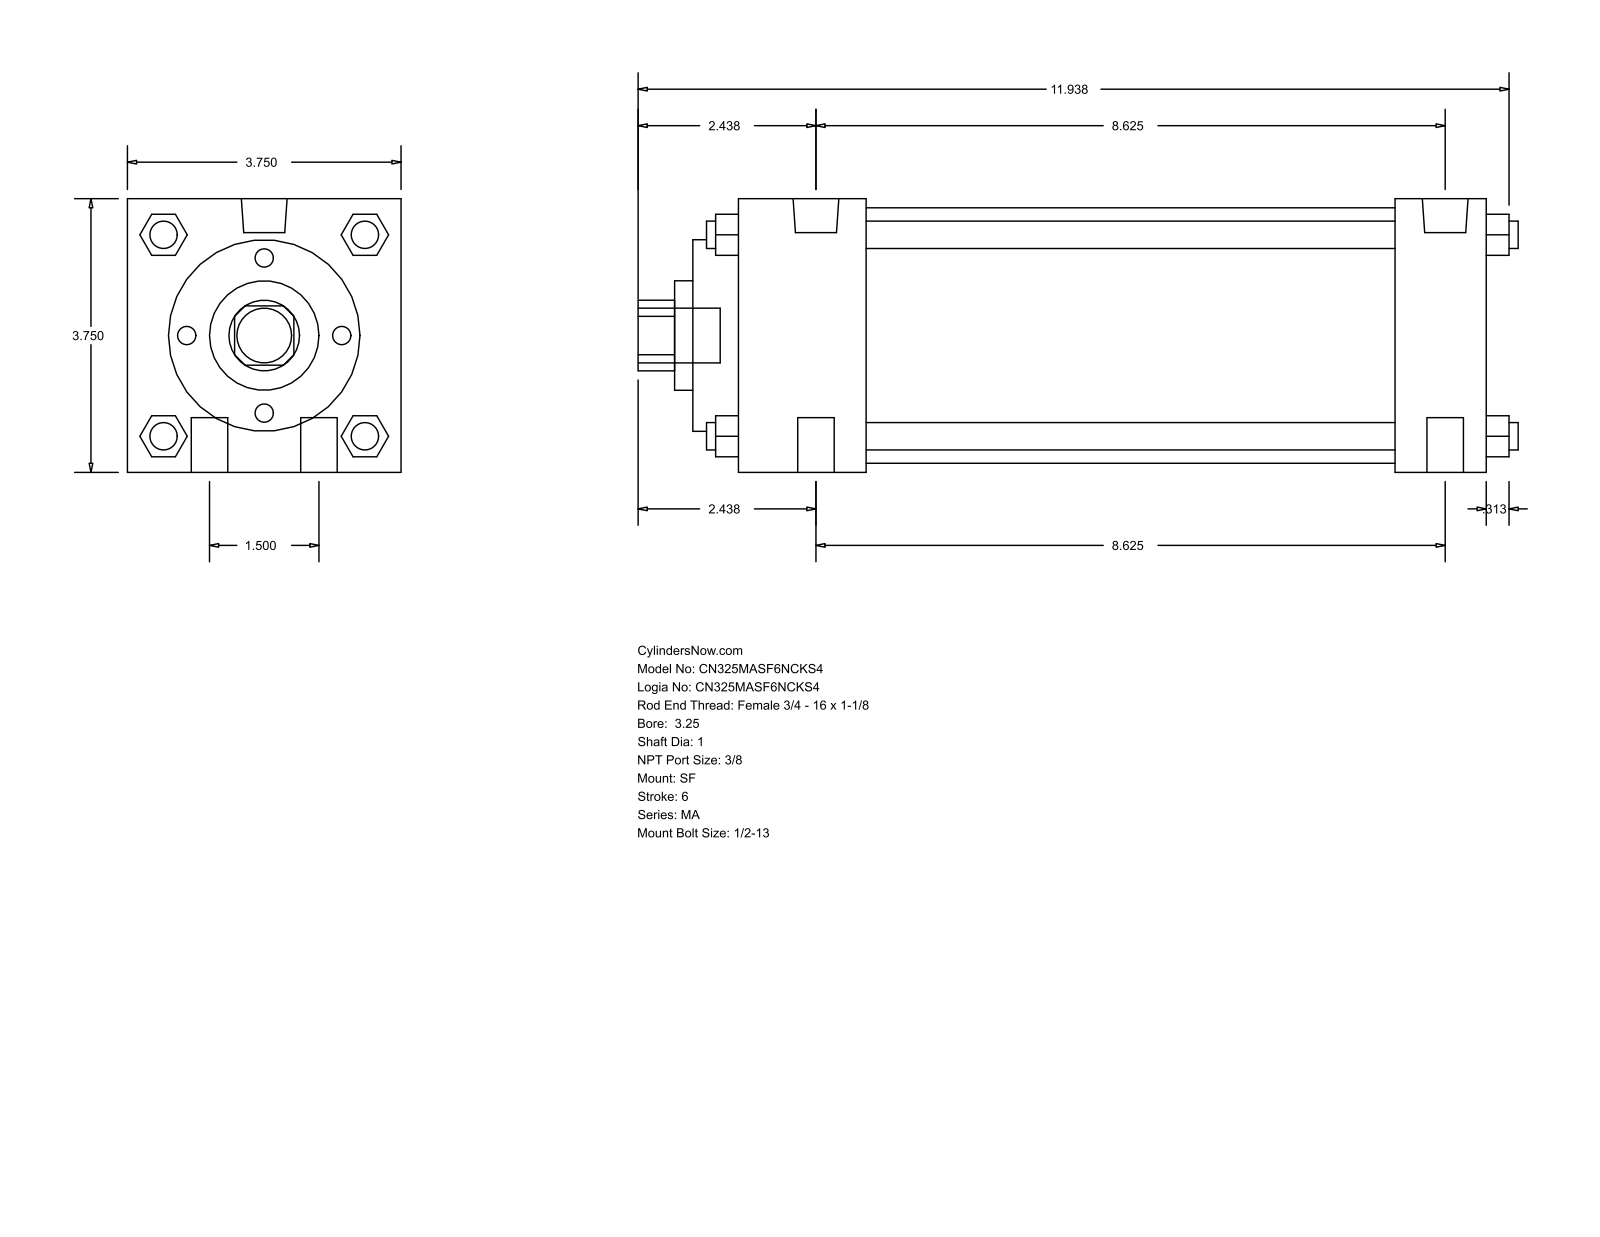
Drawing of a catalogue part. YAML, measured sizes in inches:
part_name: "MA_SF__0325_1"
step_written_by: "GSSL Pune (CONFIG_CONTROL_DESIGN)"
units: inches
bodies: {solids: 0, faces: 126, planar: 95, cylindrical: 31, other: 0}
overall_size: [12.063, 3.75, 3.75]
round_holes:
  - {diameter: 1, count: 1}
  - {diameter: 1.5, count: 1}
  - {diameter: 2.625, count: 1}
  - {diameter: 3.5, count: 1}
round_bosses_or_shafts:
  - {diameter: 0.5, count: 4}
  - {diameter: 0.375, count: 4}
  - {diameter: 0.627, count: 2}
  - {diameter: 0.437, count: 2}
  - {diameter: 0.75, count: 1}
partial_cylinders:
  - {radius: 0.484, count: 1}
face_to_face_distances: [3.75, 10.25, 10.875, 0.625, 9, 1.25, 1.75, 7.25, 8.5, 2.375]
